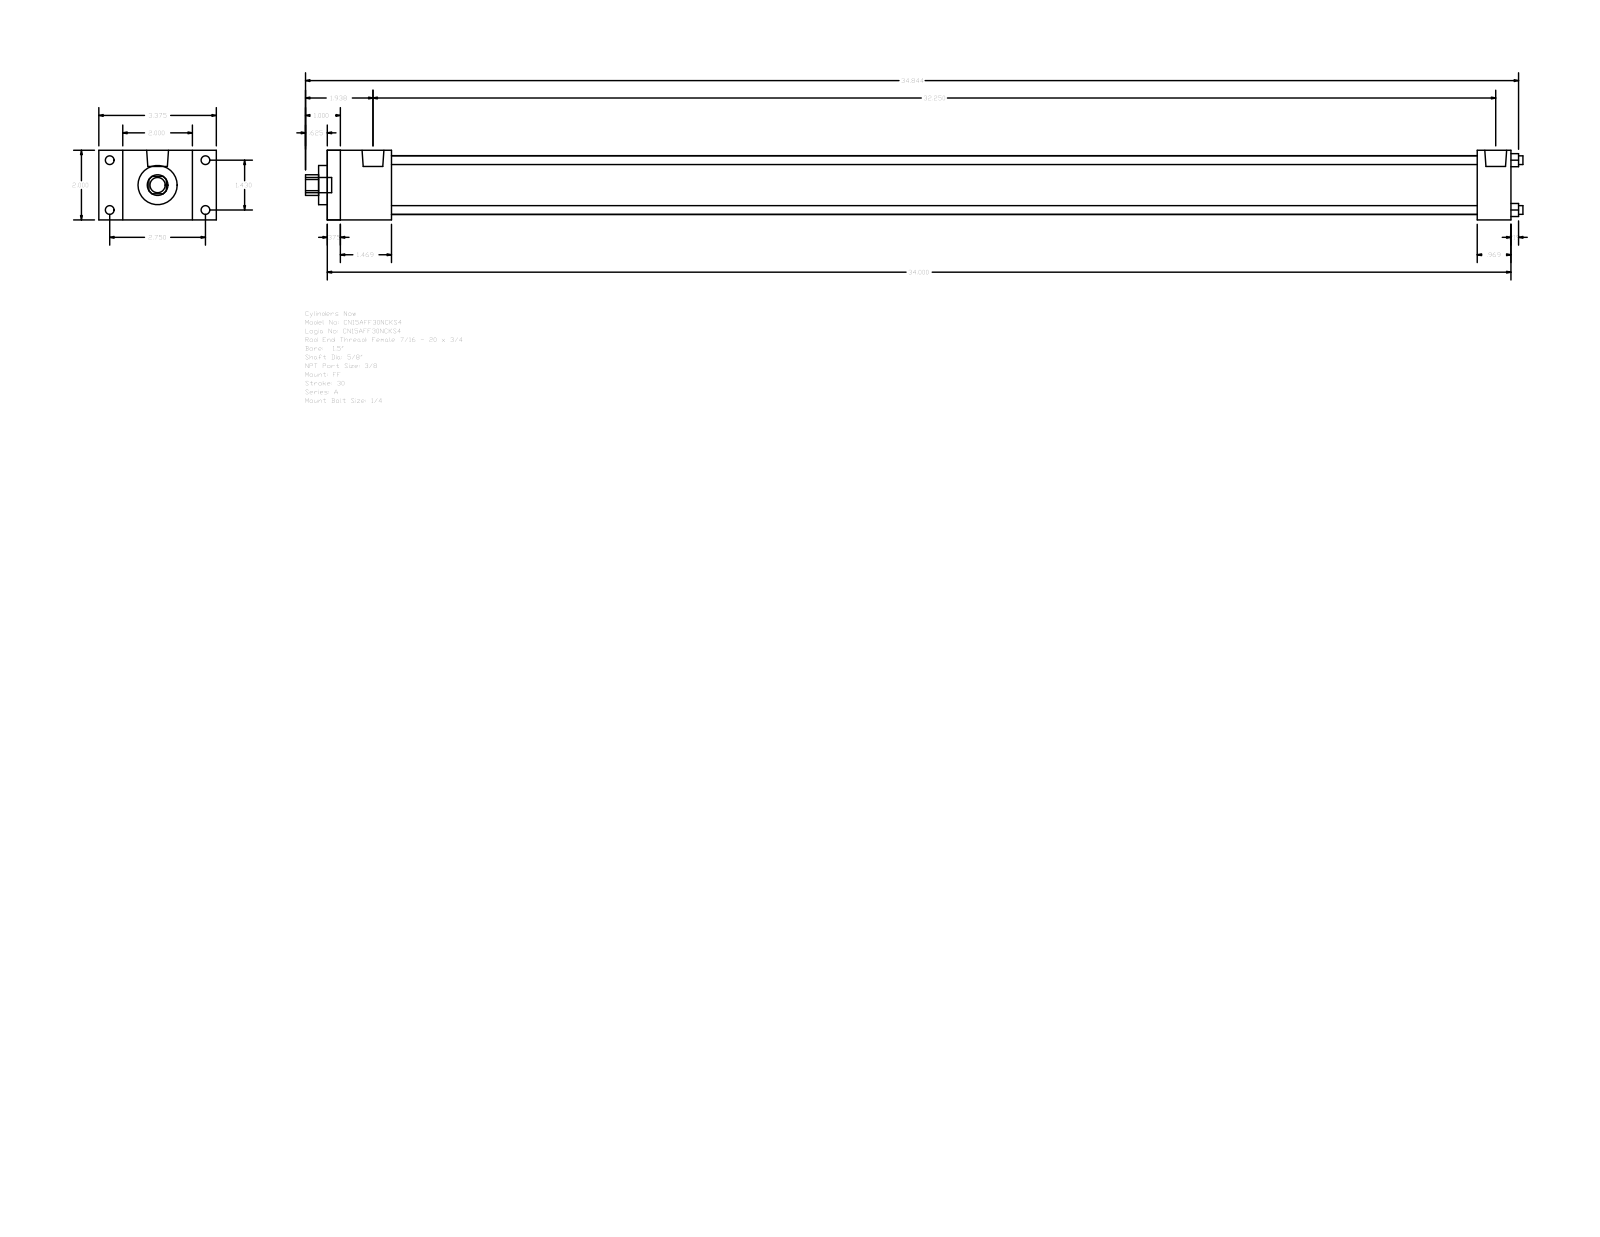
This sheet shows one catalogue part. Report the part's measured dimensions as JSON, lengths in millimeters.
{"part_name": "A_FF__0150_0.625", "step_written_by": "GSSL Pune (CONFIG_CONTROL_DESIGN)", "units": "millimeters", "bodies": {"solids": 0, "faces": 92, "planar": 64, "cylindrical": 28, "other": 0}, "overall_size": [888.21, 85.72, 50.8], "round_holes": [[6.35, 4], [15.88, 1], [28.57, 1], [42.93, 1]], "round_bosses_or_shafts": [[6.35, 4], [5.56, 4], [15.93, 2], [11.11, 1]], "partial_cylinders_radius": [[7.54, 1]], "face_to_face_distances": [50.8, 863.6, 9.52, 854.08, 46.83, 838.99, 37.31, 829.47, 792.16, 816.77], "hole_center_spacings": [25.68, 36.32, 51.36]}
